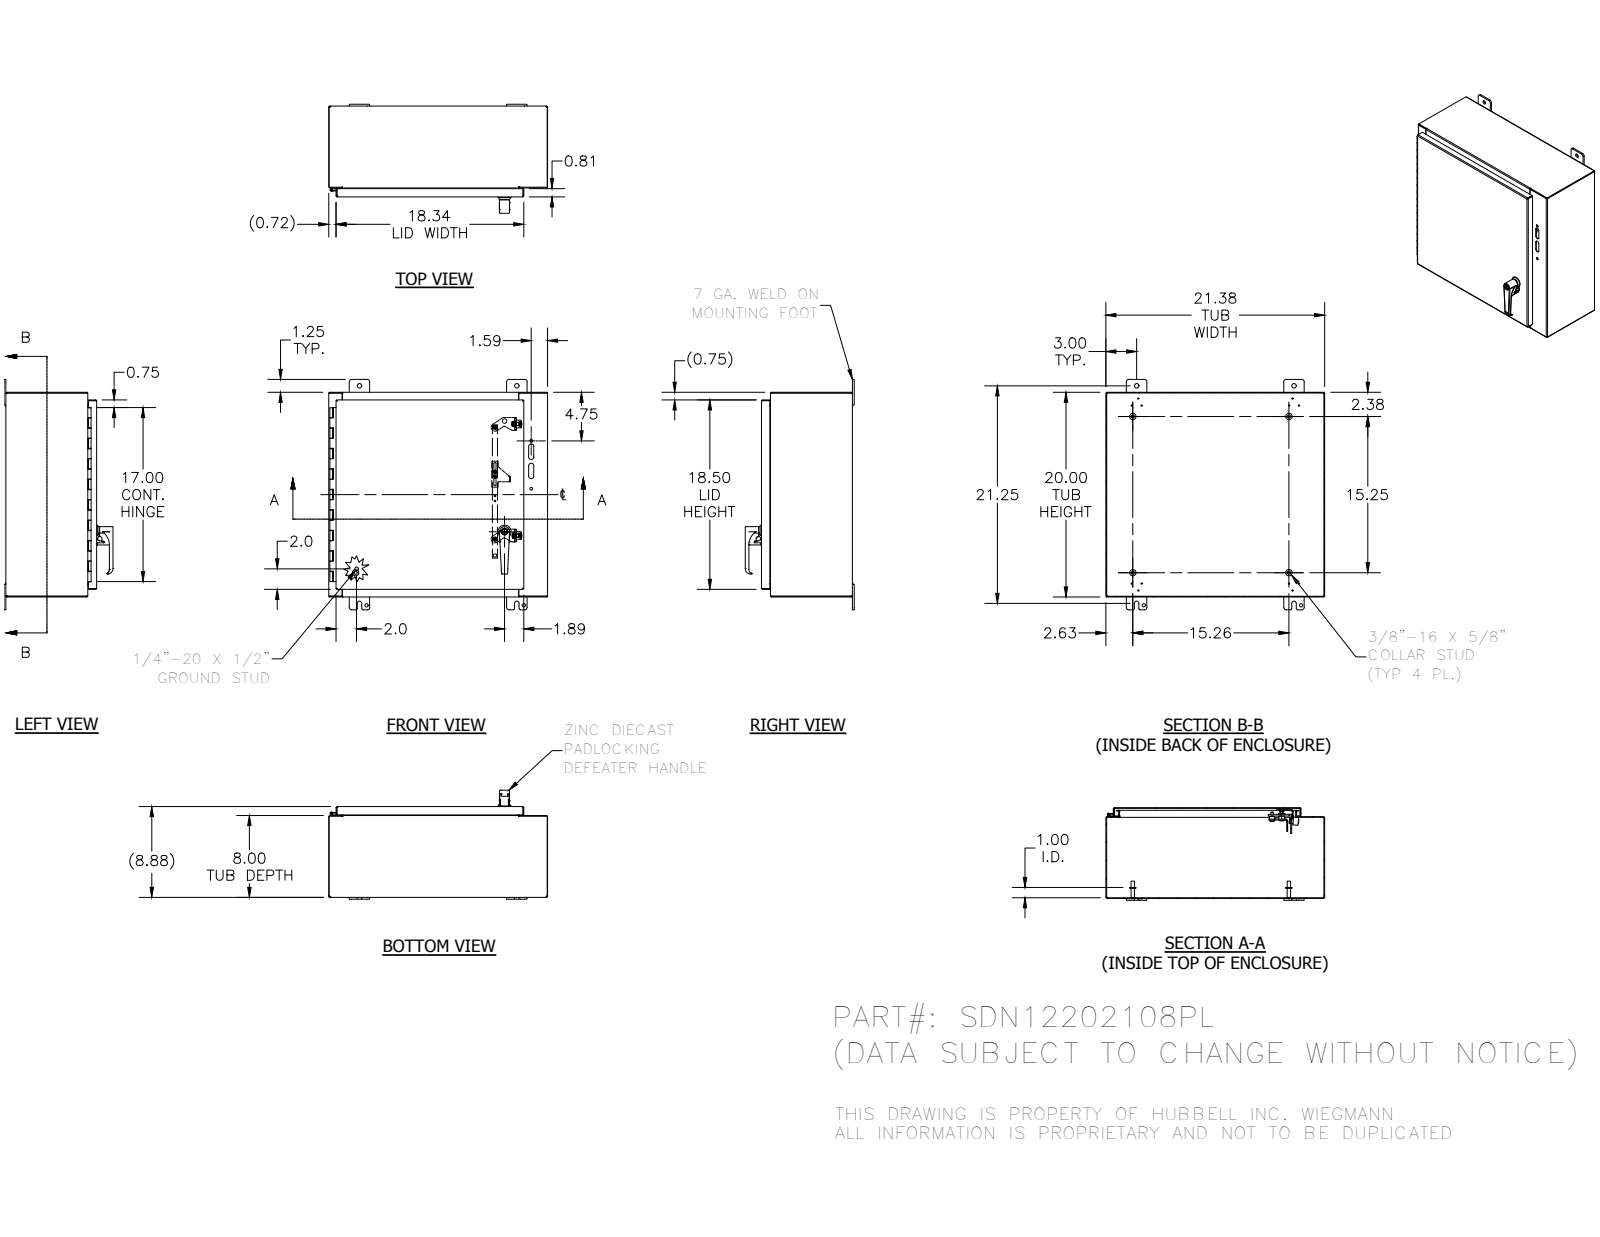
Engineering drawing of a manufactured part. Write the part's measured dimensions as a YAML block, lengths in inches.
part_name: "SDN12202108PL"
step_written_by: "SolidWorks 2019 (AUTOMOTIVE_DESIGN)"
units: inches
bodies: {solids: 49, faces: 1511, planar: 770, cylindrical: 513, other: 228}
overall_size: [22.5, 21.38, 10.649]
volume: 134
surface_area: 3550
round_holes:
  - {diameter: 0.12, count: 12}
  - {diameter: 0.145, count: 4}
  - {diameter: 0.313, count: 4}
  - {diameter: 0.438, count: 4}
  - {diameter: 0.32, count: 3}
  - {diameter: 0.156, count: 2}
  - {diameter: 0.196, count: 2}
  - {diameter: 0.211, count: 2}
  - {diameter: 0.22, count: 2}
  - {diameter: 0.281, count: 2}
  - {diameter: 0.313, count: 2}
  - {diameter: 0.45, count: 2}
round_bosses_or_shafts:
  - {diameter: 0.33, count: 5}
  - {diameter: 0.437, count: 4}
  - {diameter: 0.3, count: 4}
  - {diameter: 0.25, count: 4}
  - {diameter: 0.19, count: 4}
  - {diameter: 0.625, count: 3}
  - {diameter: 0.75, count: 2}
  - {diameter: 0.625, count: 2}
partial_cylinders:
  - {radius: 0.02, count: 38}
  - {radius: 0.012, count: 31}
  - {radius: 0.25, count: 22}
  - {radius: 0.031, count: 20}
  - {radius: 0.105, count: 20}
  - {radius: 0.125, count: 17}
  - {radius: 0.025, count: 16}
  - {radius: 0.07, count: 8}
face_to_face_distances: [0.074, 8.801, 8.727, 19.926, 8.875, 21.306, 7.926, 0.875, 20, 19.852]
hole_center_spacings: [10.9, 0.759, 14.752, 15.38, 17.38, 18.069, 18.077, 18.751]
